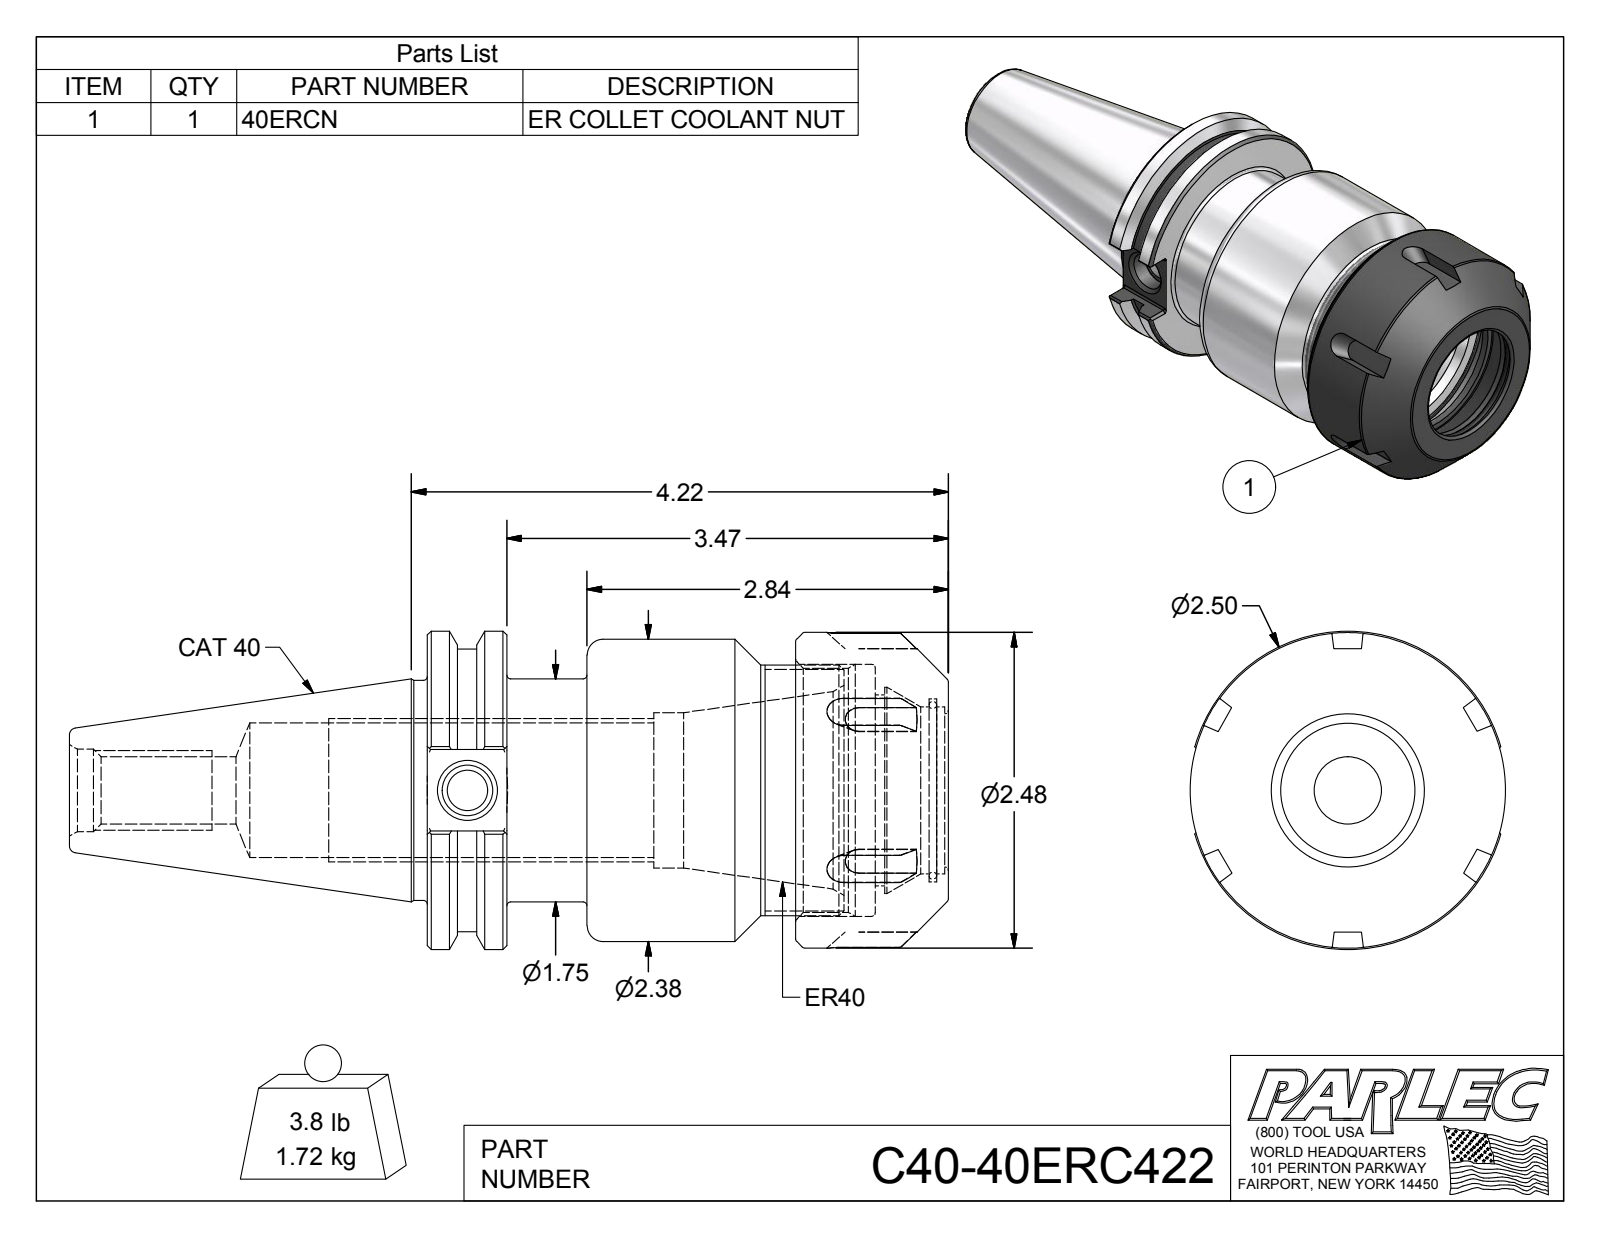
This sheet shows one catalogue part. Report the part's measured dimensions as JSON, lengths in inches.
{"part_name": "C40-40ERC422; C40-40ER4-1; 40ERCN", "step_written_by": "Autodesk Inventor 2012 (AUTOMOTIVE_DESIGN)", "units": "inches", "bodies": {"solids": 2, "faces": 143, "planar": 59, "cylindrical": 36, "other": 48}, "overall_size": [6.908, 2.5, 2.479], "volume_in3": 13.34, "surface_area_in2": 86.87, "round_holes": [[0.315, 1], [0.399, 1], [0.527, 1], [0.648, 1], [1.057, 1], [1.22, 1], [1.313, 1], [1.437, 1], [1.5, 1], [1.62, 1], [1.916, 1], [1.98, 1]], "round_bosses_or_shafts": [[2.5, 1], [2.48, 1], [2.375, 1], [2.219, 1], [1.969, 1], [1.75, 1], [1.73, 1]], "partial_cylinders_radius": [[0.02, 12]], "face_to_face_distances": [0.625, 2.895, 3.52, 4.095, 3.47, 0.575, 1.255, 0.63, 2.265, 2.84]}
